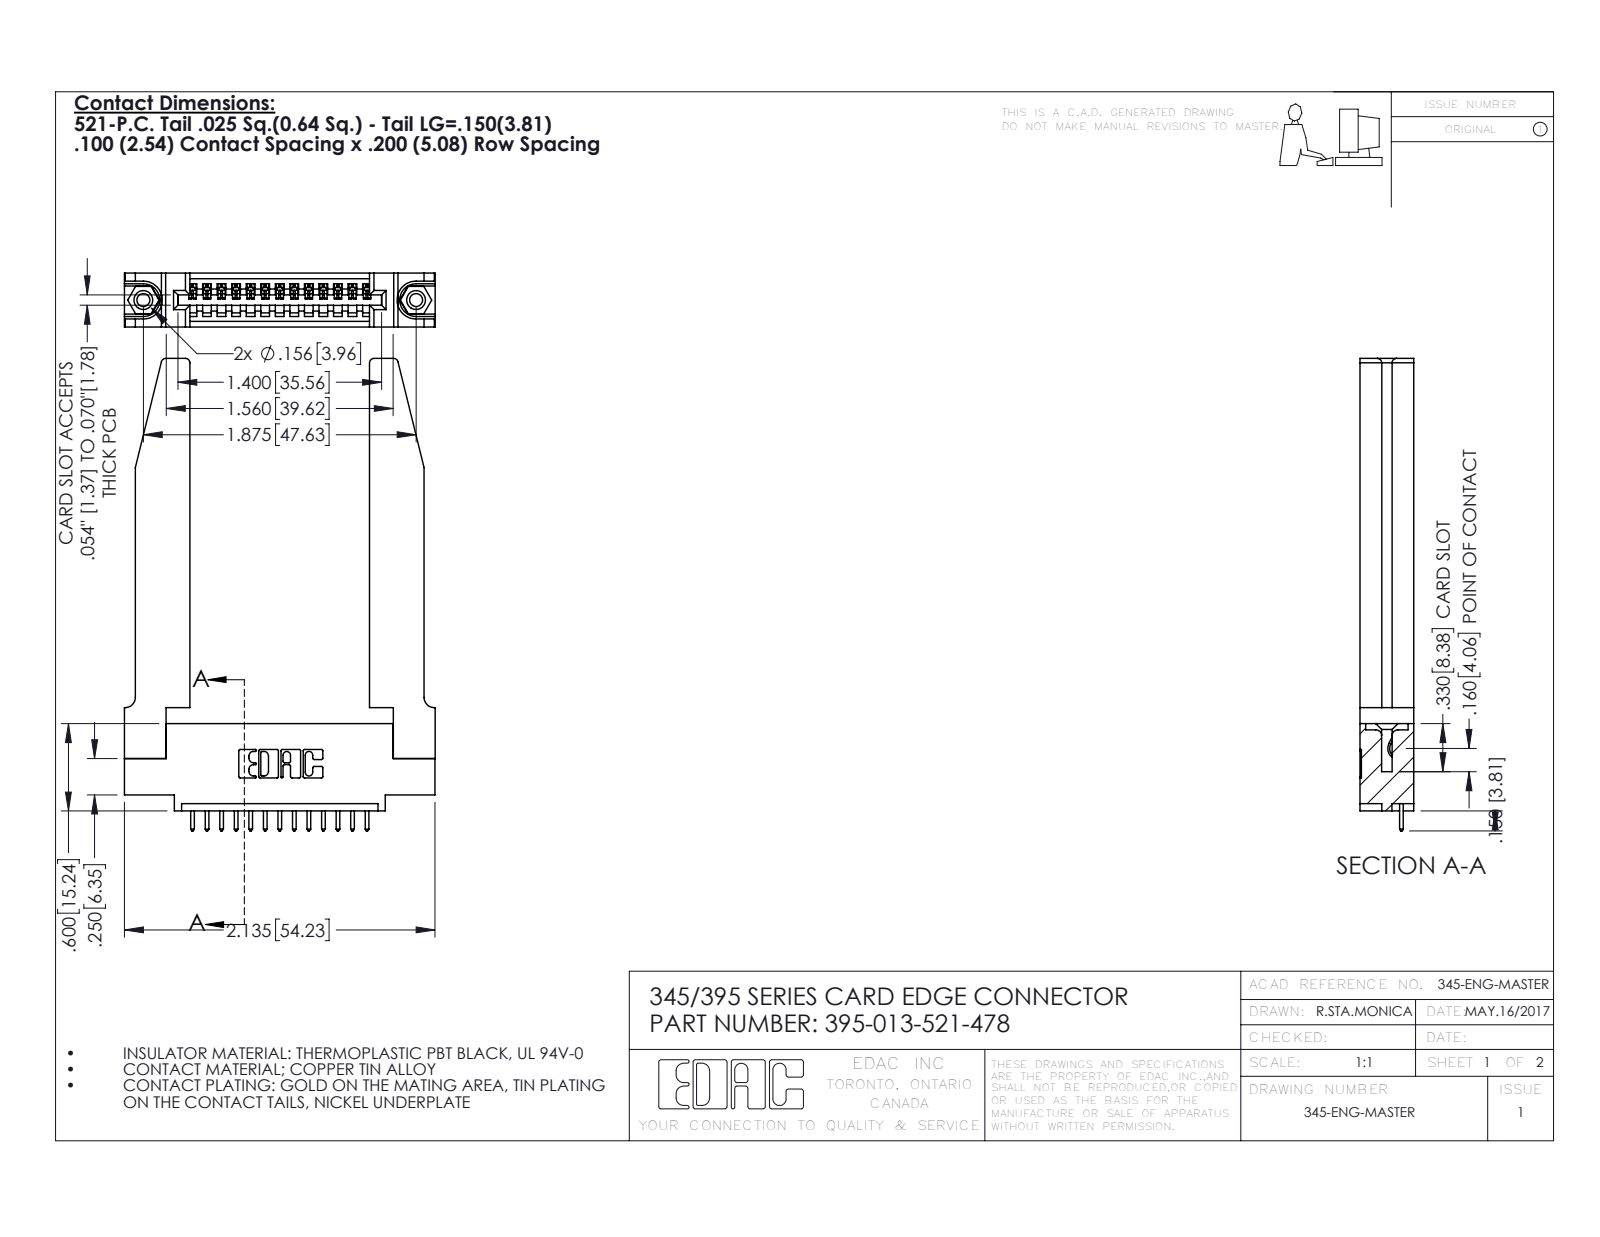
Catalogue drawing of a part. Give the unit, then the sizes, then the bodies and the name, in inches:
Units: inches
Overall size (bounding box): 3.247 × 2.136 × 0.37
Round holes (diameter × count): ⌀0.089 ×2, ⌀0.125 ×2, ⌀0.156 ×2, ⌀0.064 ×1
Round bosses / shafts (diameter × count): ⌀0.155 ×2
Partial cylindrical surfaces — rounded edges, fillets, slot ends (radius × count): R0.006 ×26, R0.01 ×26, R0.01 ×22, R0.03 ×8, R0.007 ×6, R0.031 ×6, R0.026 ×3, R0.031 ×2
Main face-to-face distances: 0.37, 0.072, 0.298, 0.148, 0.15, 0.22, 0.077, 1.235, 0.2, 0.098
Hole centre spacings: 0.27, 1.643, 1.875
Volume: 0.767 in³ · Surface area: 19.8 in²
Bodies: 18 solids, 1118 faces (746 planar, 320 cylindrical, 52 other)
Part name (STEP PRODUCT): 395-013-521-478; 345-292-001_345-293-121; 345-220-078_345-220-078; 345-250-001_345-250-001-102 (+1 more)
STEP written by: SolidWorks 2016 (CONFIG_CONTROL_DESIGN)
